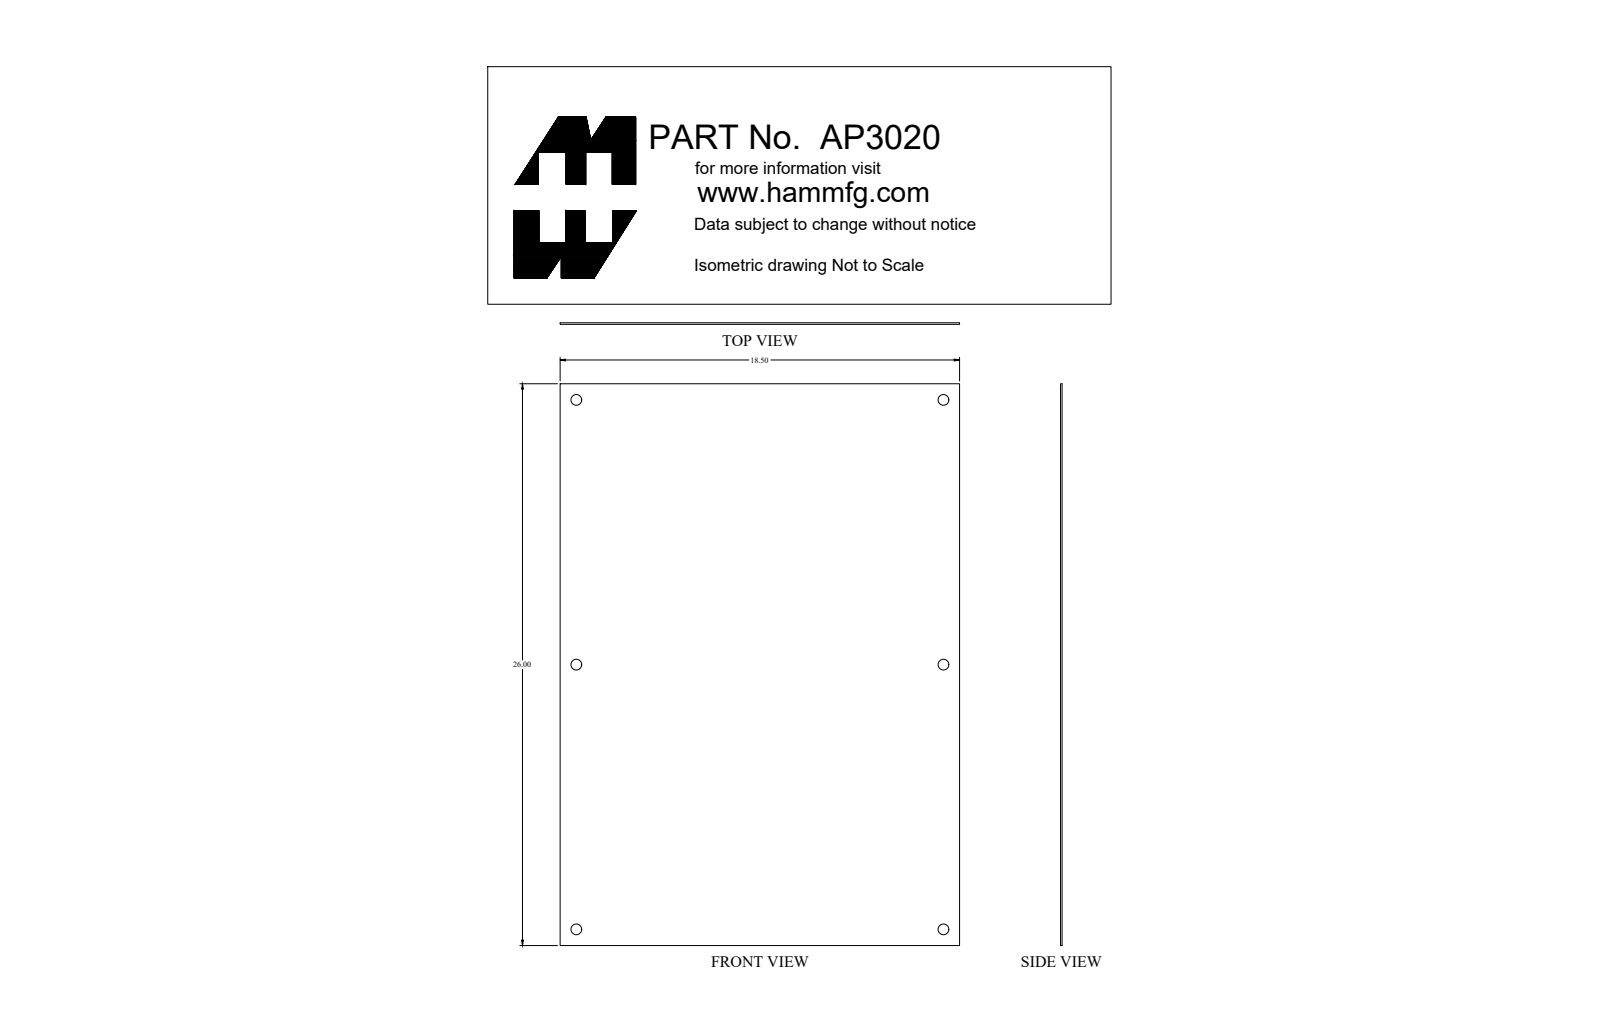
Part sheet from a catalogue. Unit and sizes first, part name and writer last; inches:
Units: inches
Overall size (bounding box): 26 × 18.5 × 0.072
Round holes (diameter × count): ⌀0.5 ×6
Main face-to-face distances: 0.072, 18.5, 26
Hole centre spacings: 12.25, 20.954, 17, 24.5, 29.82
Volume: 34.55 in³ · Surface area: 966.7 in²
Bodies: 1 solid, 18 faces (6 planar, 12 cylindrical, 0 other)
Part name (STEP PRODUCT): AP3020_Default
STEP written by: SolidWorks 2019 (CONFIG_CONTROL_DESIGN)
